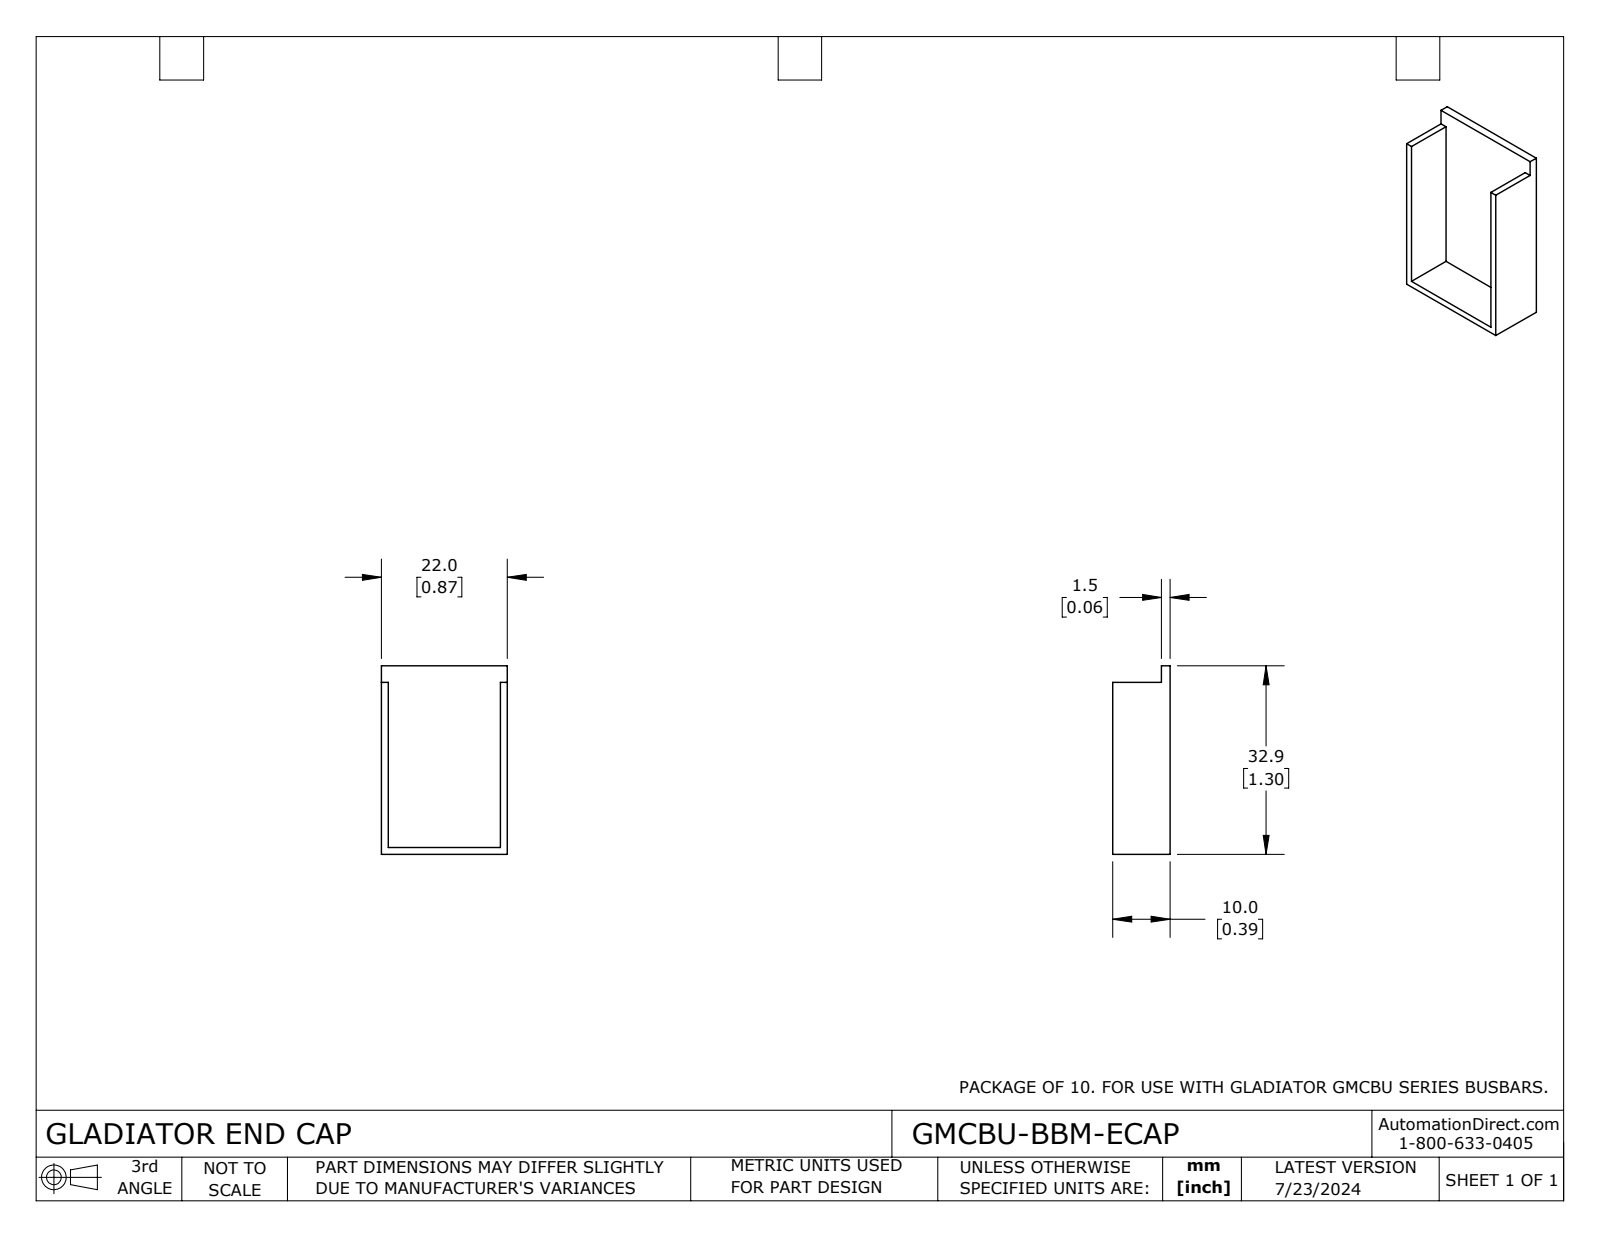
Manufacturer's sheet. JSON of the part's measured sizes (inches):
{"part_name": "GMCBU-BBM-ECAP", "step_written_by": "SolidWorks 2023 (CONFIG_CONTROL_DESIGN)", "units": "inches", "bodies": {"solids": 1, "faces": 12, "planar": 12, "cylindrical": 0, "other": 0}, "overall_size": [1.295, 0.866, 0.394], "volume_in3": 0.116, "surface_area_in2": 4.628, "face_to_face_distances": [0.047, 0.059, 0.819, 0.866, 0.772, 0.335, 0.394, 1.295, 1.248, 1.181]}
